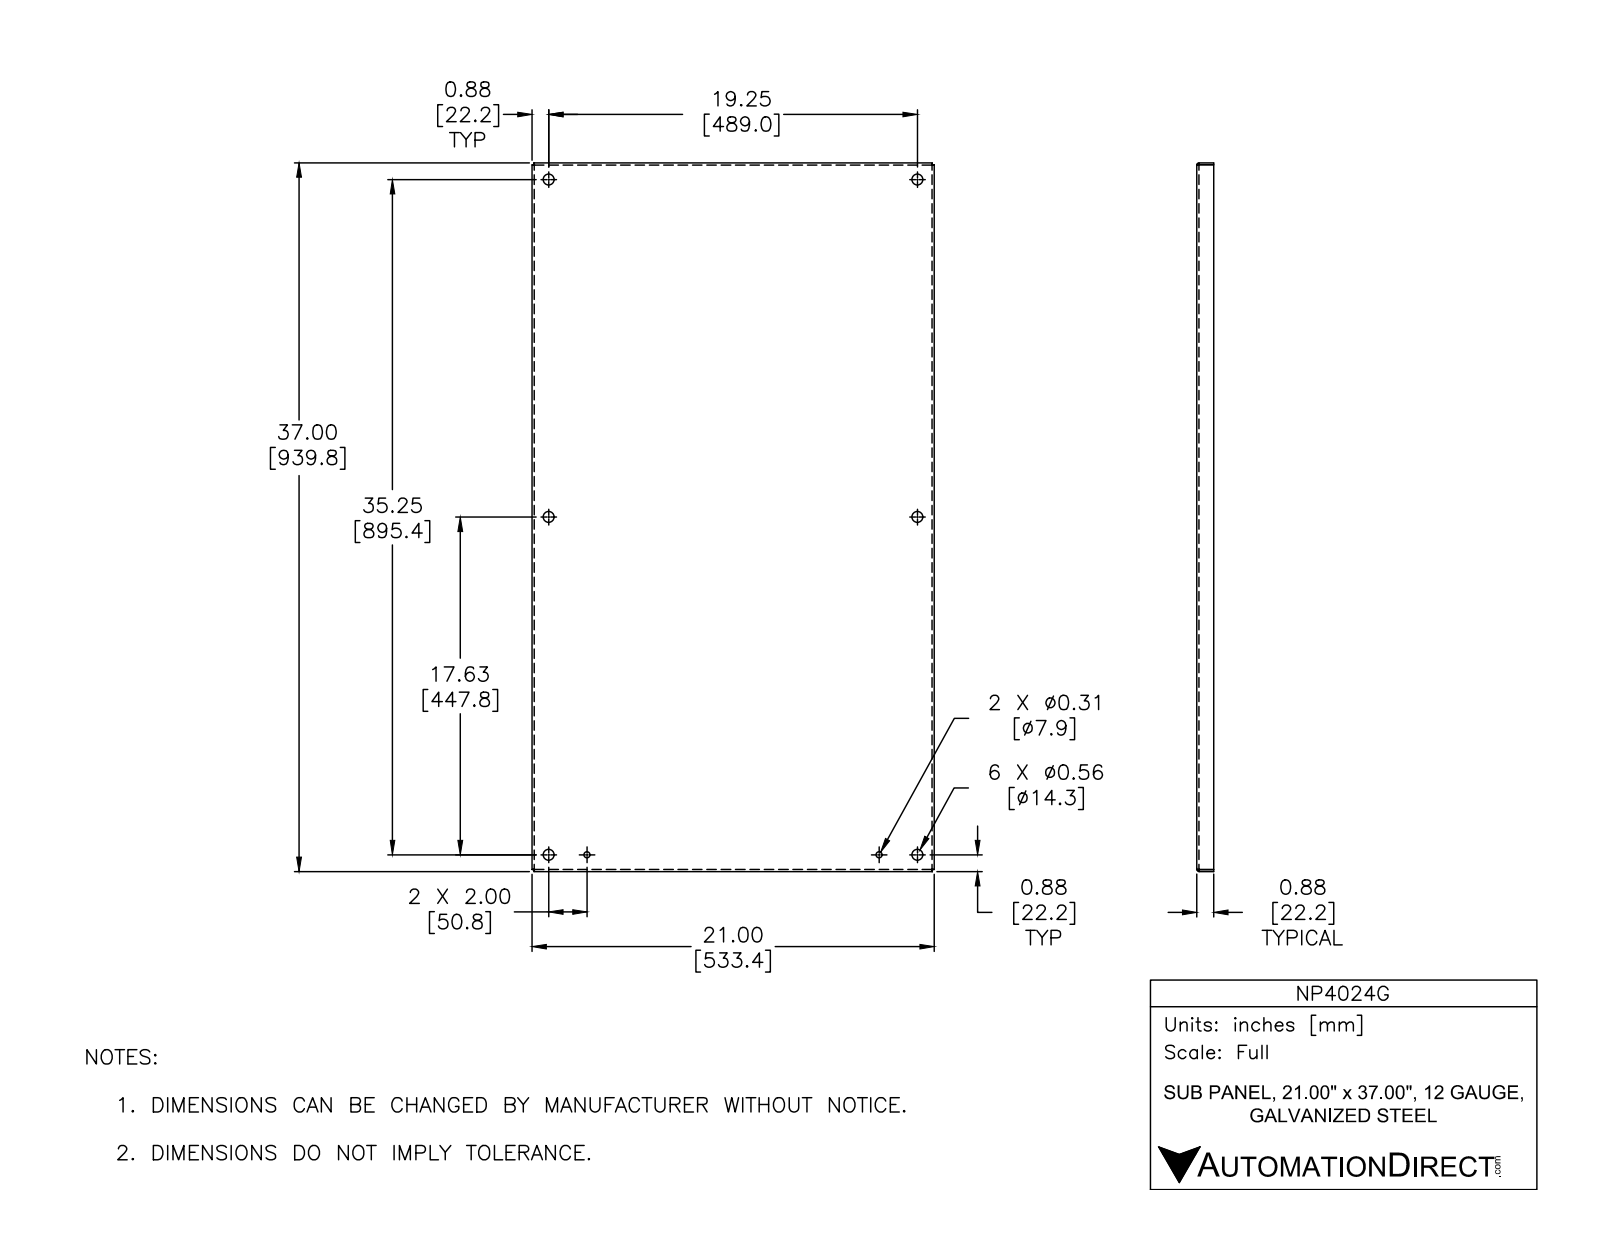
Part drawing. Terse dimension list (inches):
name: NP4024G
written by: Autodesk Inventor 2012 (AUTOMOTIVE_DESIGN)
unit: in
bodies: 1 solid, 46 faces (22 planar, 16 cylindrical, 8 other)
size: 37 × 21 × 0.875
volume: 80.71 in³; area: 1 735 in²
holes: 6× ⌀0.563, 2× ⌀0.312
rounds: 4× R0.031, 4× R0.125
face distances: 0.094, 20.906, 36.906, 21, 20.813, 37, 36.813, 0.781, 0.875, 0.105
hole spacings: 17.625, 26.1, 19.25, 24.662, 35.25, 40.164, 2, 2
